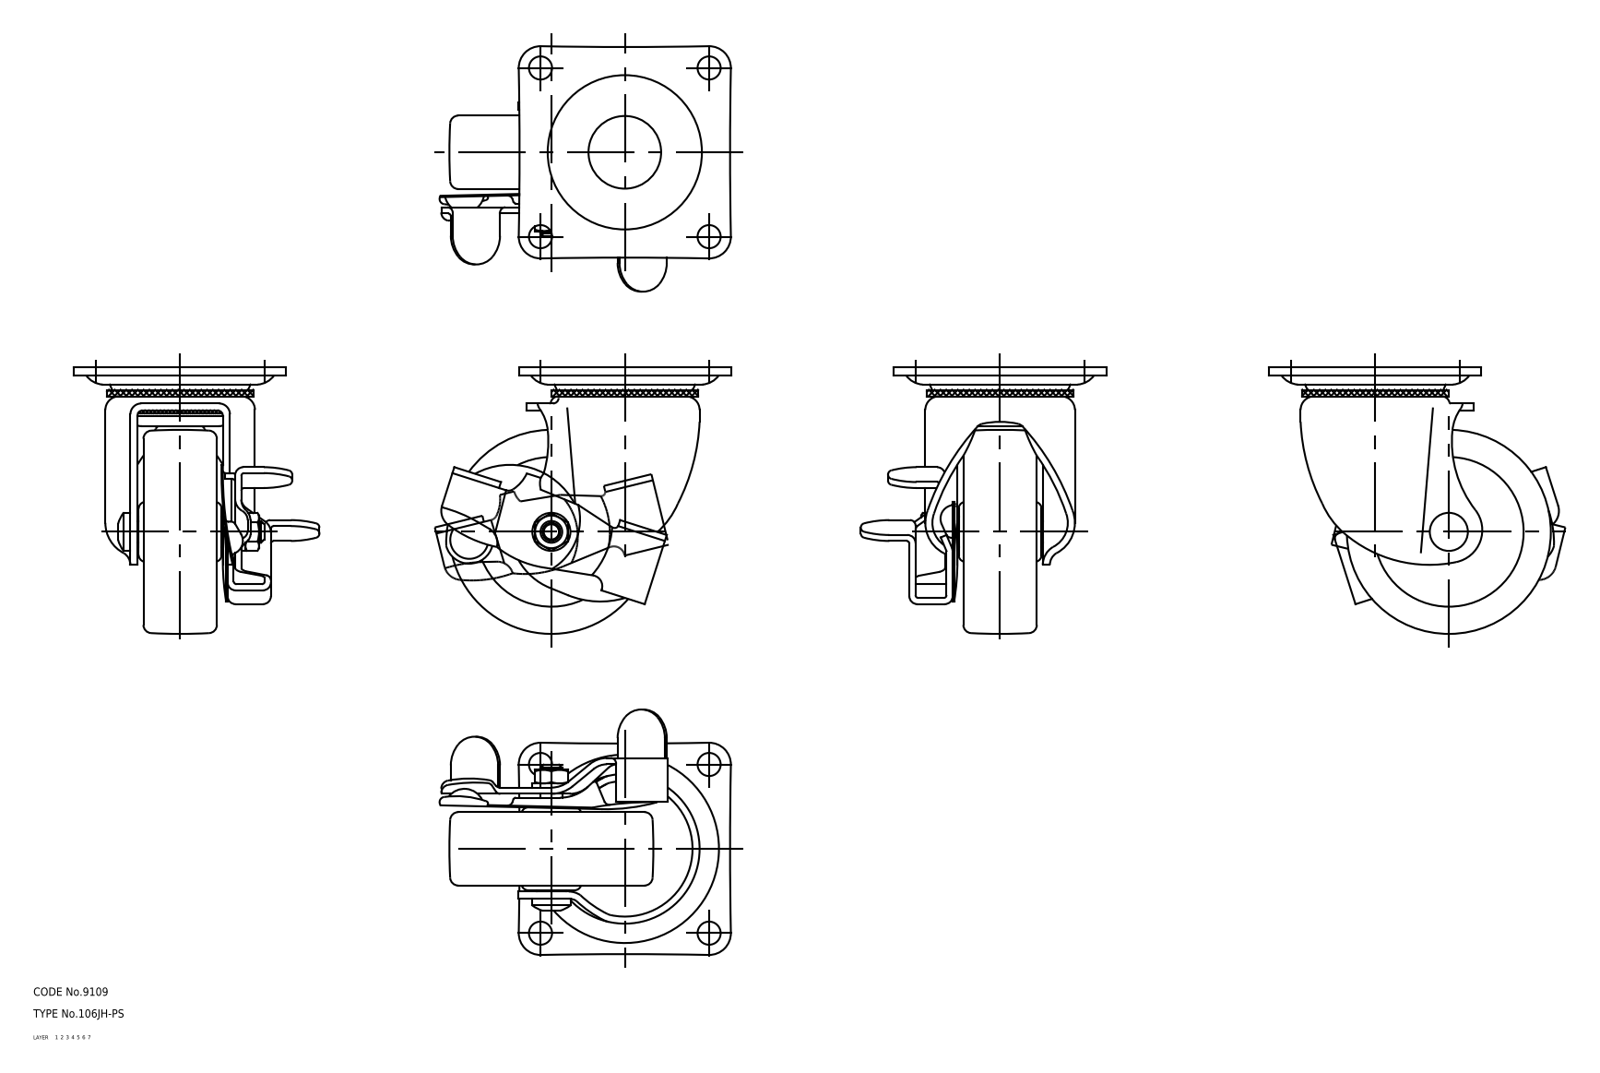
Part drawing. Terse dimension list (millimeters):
name: lever; plate; wheel; mounting plate (+3 more)
written by: CADfix (AUTOMOTIVE_DESIGN)
unit: mm
bodies: 7 solids, 409 faces (0 planar, 0 cylindrical, 409 other)
size: 106.49 × 98 × 90.21
volume: 175 855 mm³; area: 70 340 mm²
